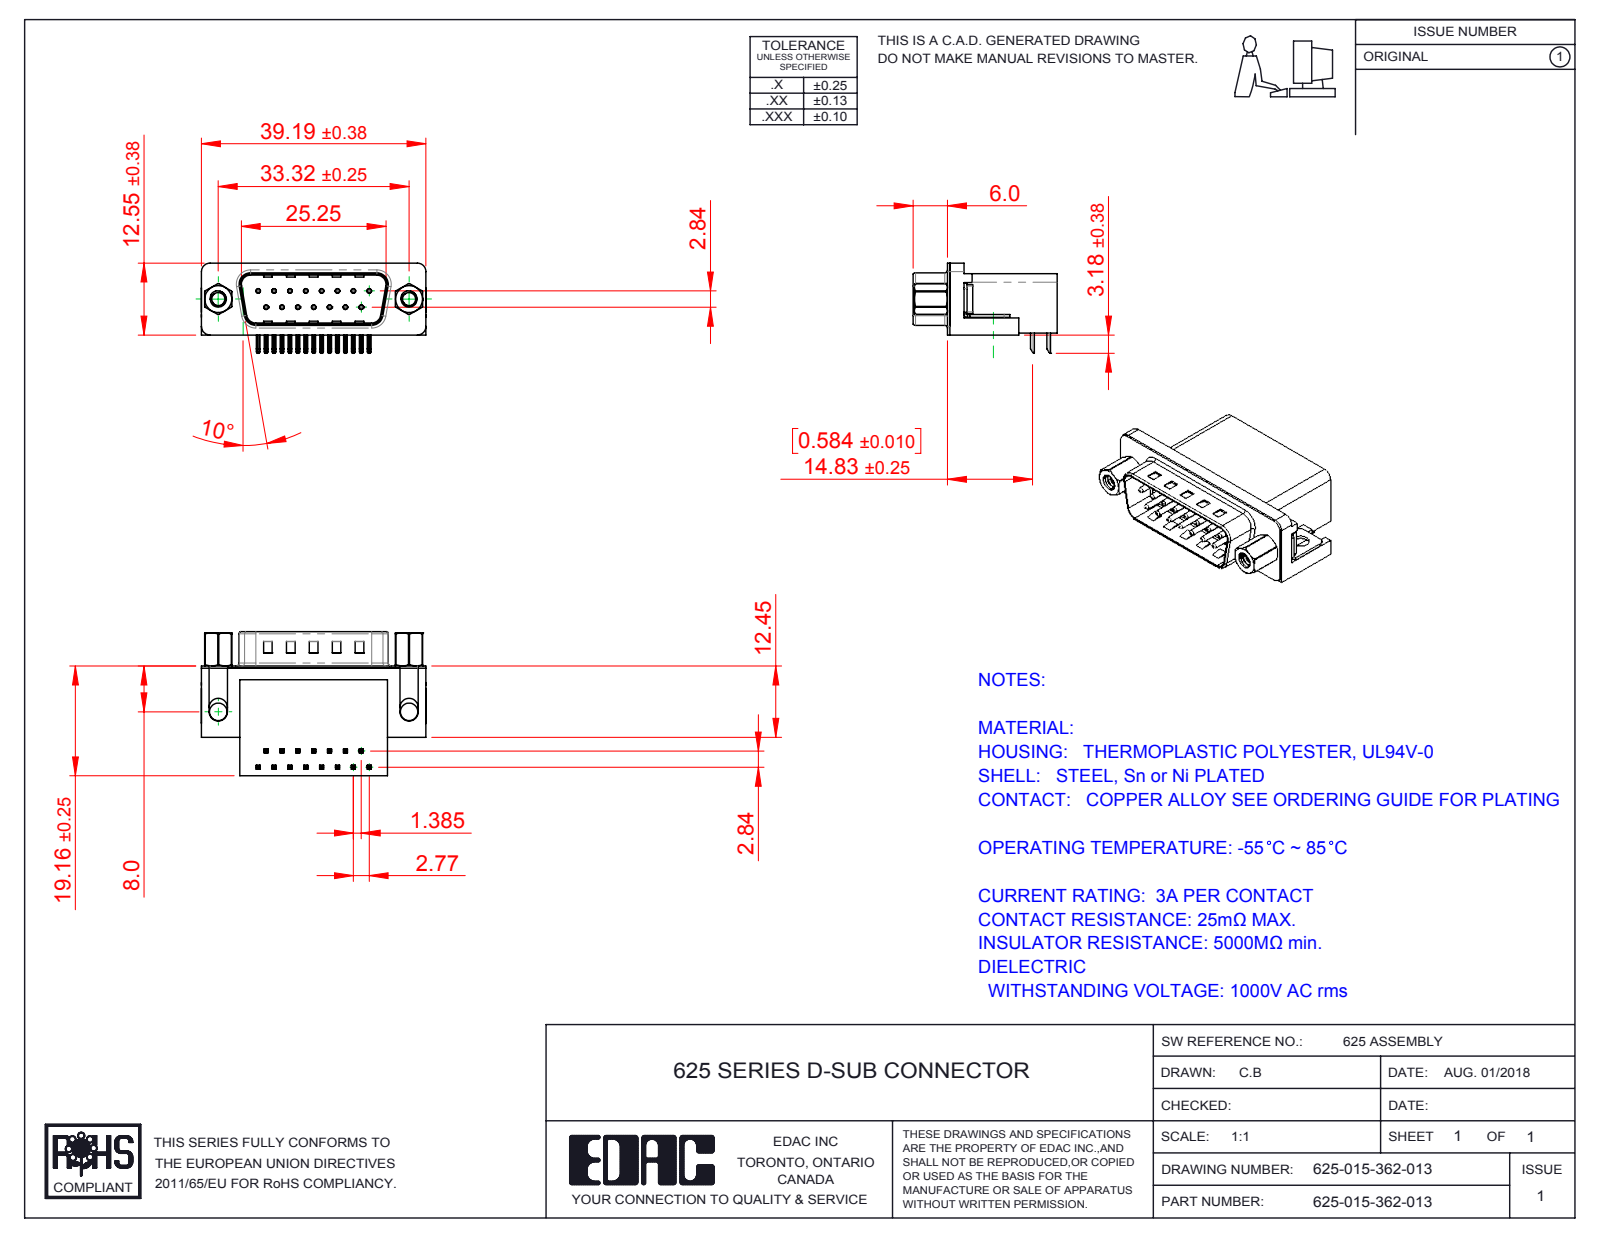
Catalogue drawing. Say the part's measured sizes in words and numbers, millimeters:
The part is named "625 Contact Bottom; 625 Shell_15 Socket; 625 Housing_15 Socket; 625 4-40 Hex Standoff 5 (+4 more)". Its 3-D file was written by "SolidWorks 2016 (CONFIG_CONTROL_DESIGN)". It is 23 solids with 1605 faces: 915 planar, 519 cylindrical and 171 other. Overall it measures 39.22 by 25.16 by 15.73 millimeters. Its volume is 6 454 cubic millimeters and its surface area 6 895 square millimeters. Round holes: 15 of diameter 0.35, 15 of diameter 0.8, 2 of diameter 2.26, 2 of diameter 2.29, 2 of diameter 3.05, 2 of diameter 4, 2 of diameter 4.8, 2 of diameter 5. Round bosses or shafts: 15 of diameter 0.75, 2 of diameter 4.9, 2 of diameter 4.75, 2 of diameter 3.9, 2 of diameter 2.79. Partial cylindrical surfaces (rounded edges, fillets, slot ends): 68 of radius 0.25, 30 of radius 0.12, 16 of radius 1, 9 of radius 0.5, 8 of radius 1.6, 6 of radius 1.5, 4 of radius 0.9, 4 of radius 2. The main face-to-face distances are 0.4, 10.35, 18.76, 2.1, 19.16, 10.46, 1.7, 10.86, 8.76, 16.26. The hole center spacings are 3.16, 2.77, 5.54, 8.31, 11.08, 5.03, 5.04, 7.48.
